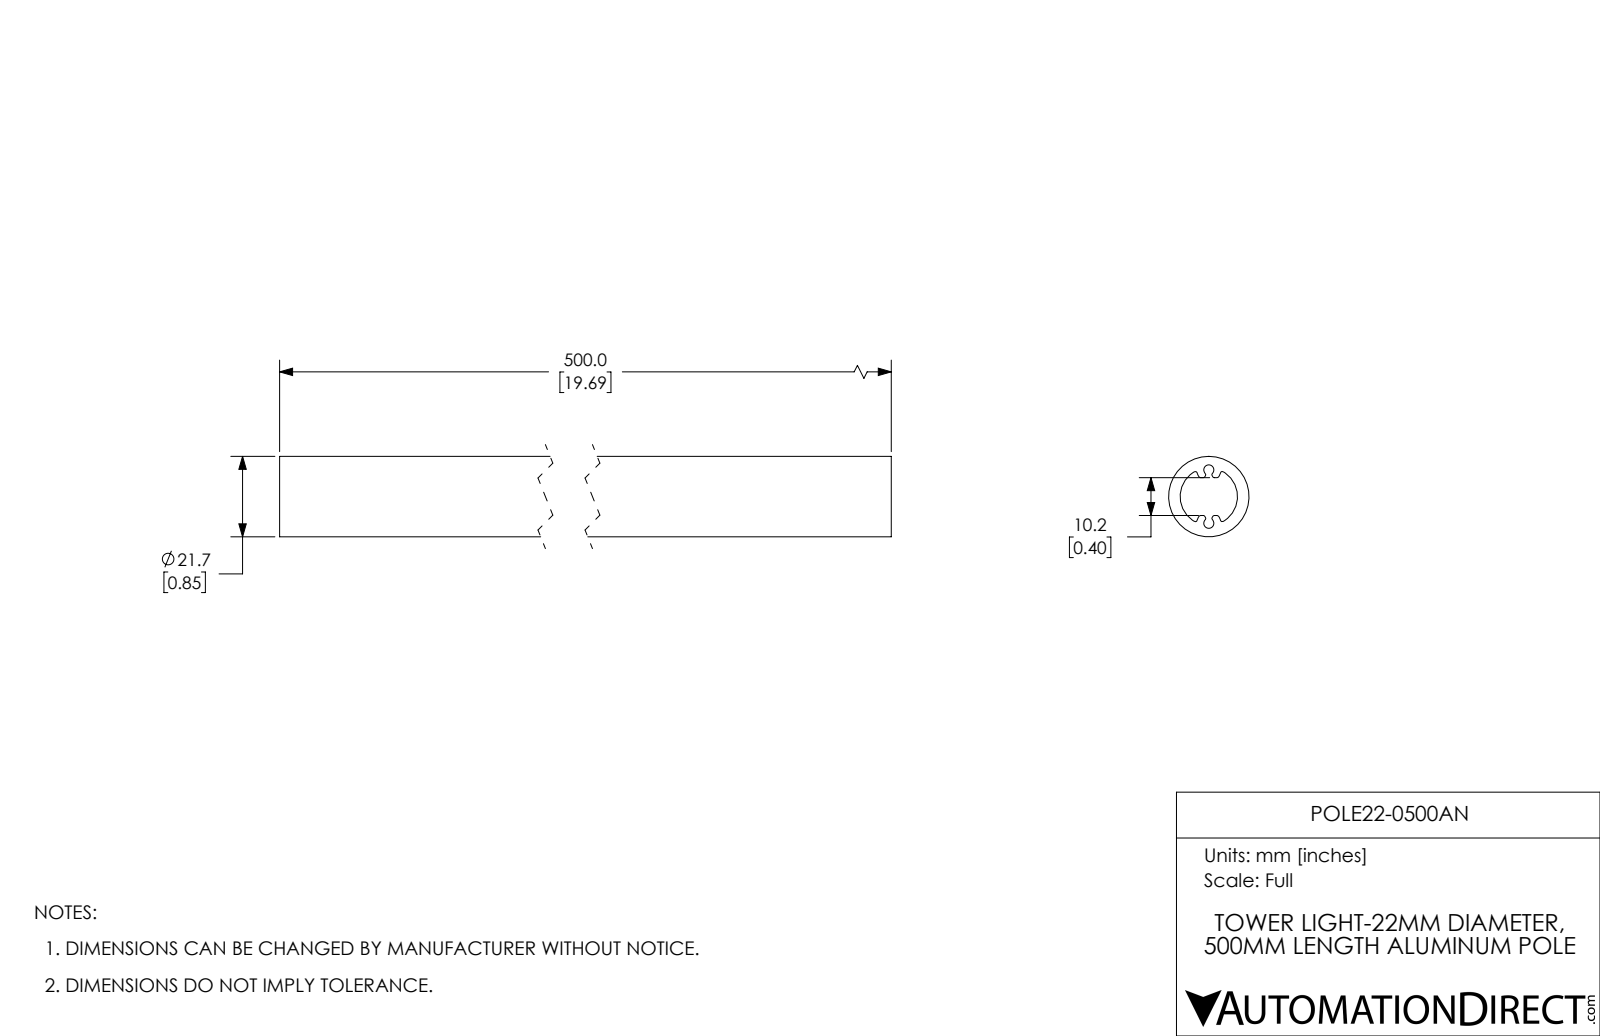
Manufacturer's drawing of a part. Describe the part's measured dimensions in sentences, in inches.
The part is named "POLE22-0500AN". Its 3-D file was written by "SolidWorks 2017 (AUTOMOTIVE_DESIGN)". It is 1 solid with 8 faces: 2 planar, 2 cylindrical and 4 other. Overall it measures 19.685 by 0.854 by 0.854 inches. Its volume is 5.974 cubic inches and its surface area 103.6 square inches. Round bosses or shafts: 1 of diameter 0.854. The main face-to-face distances are 19.685.
